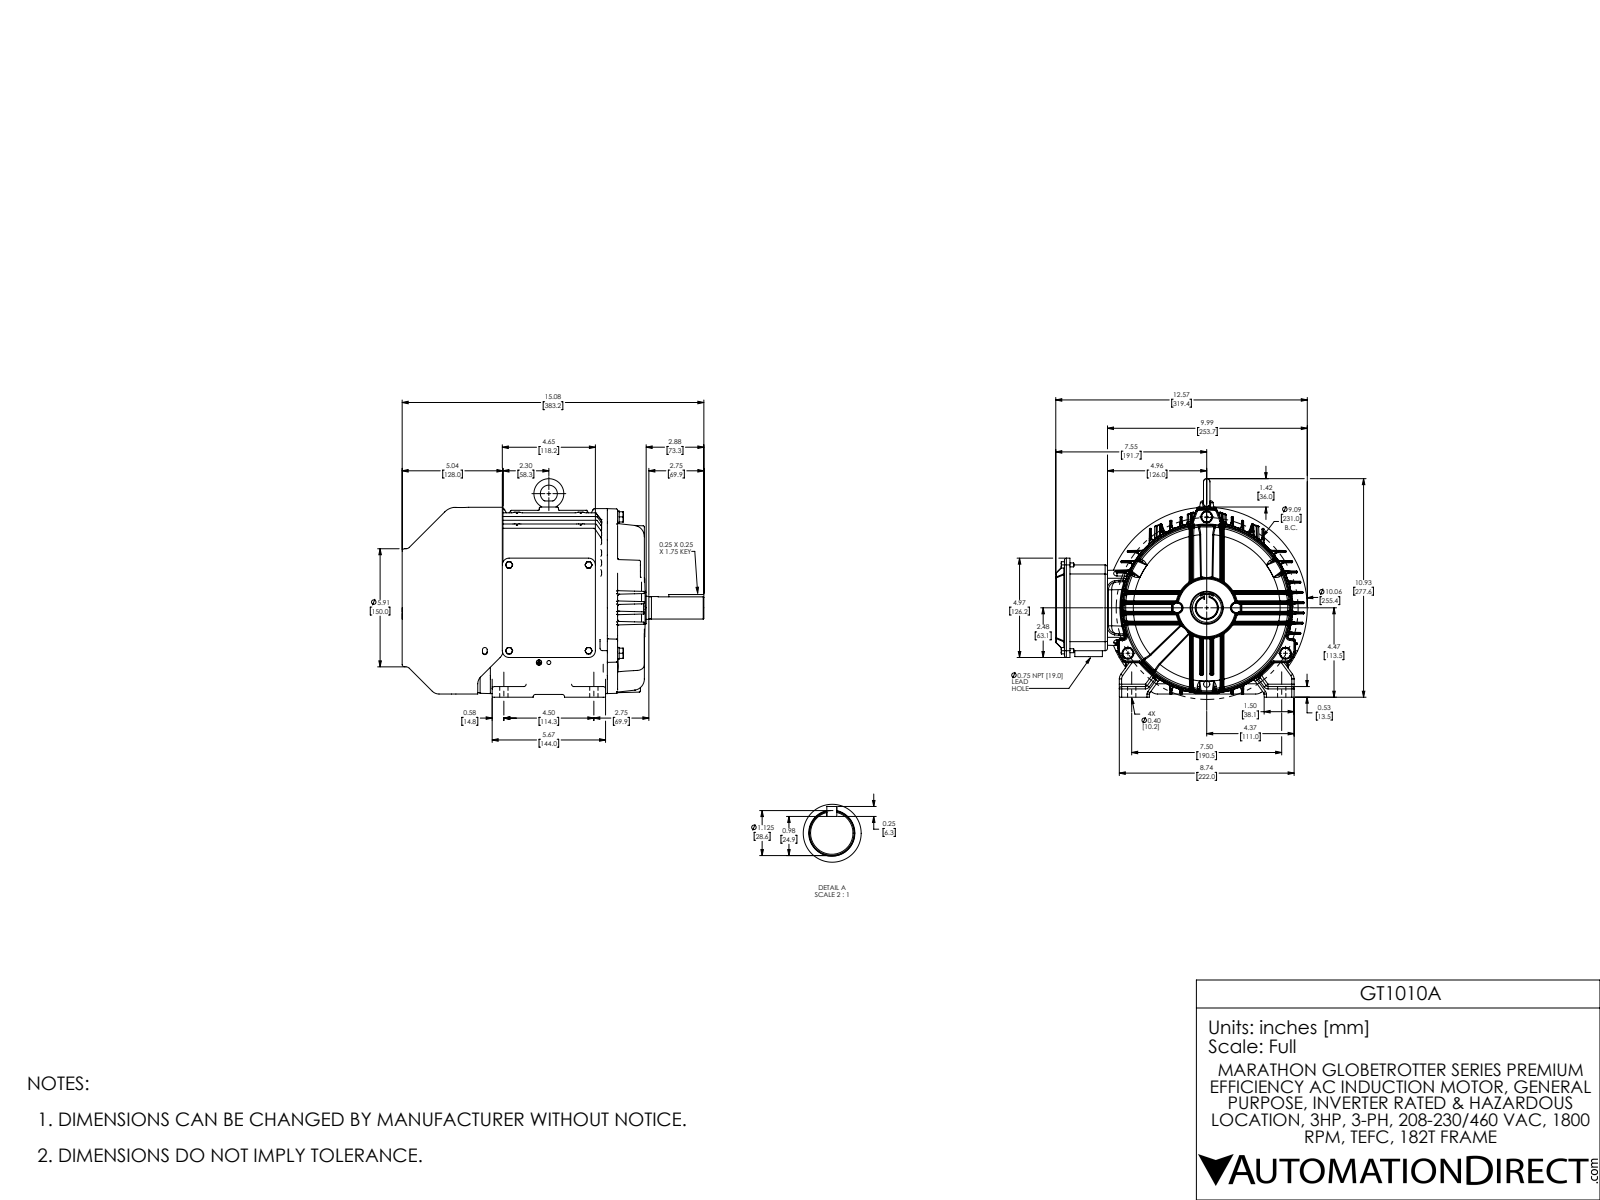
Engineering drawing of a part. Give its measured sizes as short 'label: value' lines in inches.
name: SS620855-182T_Rev00 r1 Nice Coord
written by: SolidWorks 2017 (AUTOMOTIVE_DESIGN)
unit: in
bodies: 1 solid, 4870 faces (693 planar, 1635 cylindrical, 2542 other)
size: 15.085 × 12.575 × 10.927
volume: 791.1 in³; area: 776.8 in²
holes: 8× ⌀0.079, 4× ⌀0.413, 2× ⌀0.248, 1× ⌀0.157, 1× ⌀0.197, 1× ⌀0.311, 1× ⌀0.748, 1× ⌀1.591
bosses: 4× ⌀0.197, 3× ⌀0.591, 2× ⌀0.268, 1× ⌀10.055, 1× ⌀8.583, 1× ⌀5.906, 1× ⌀1.654, 1× ⌀1.378
rounds: 288× R0.118, 104× R0.039, 72× R1.32, 72× R1.419, 40× R0.079, 39× R0.059, 28× R0.094, 20× R0.02
face distances: 0.512, 4.992, 0.118, 4.874, 0.506, 0.159, 0.508, 4.606, 4.341, 2.569
hole spacings: 1.732, 3.189, 3.629, 4.373, 0.492, 4.314, 4.5, 7.5
